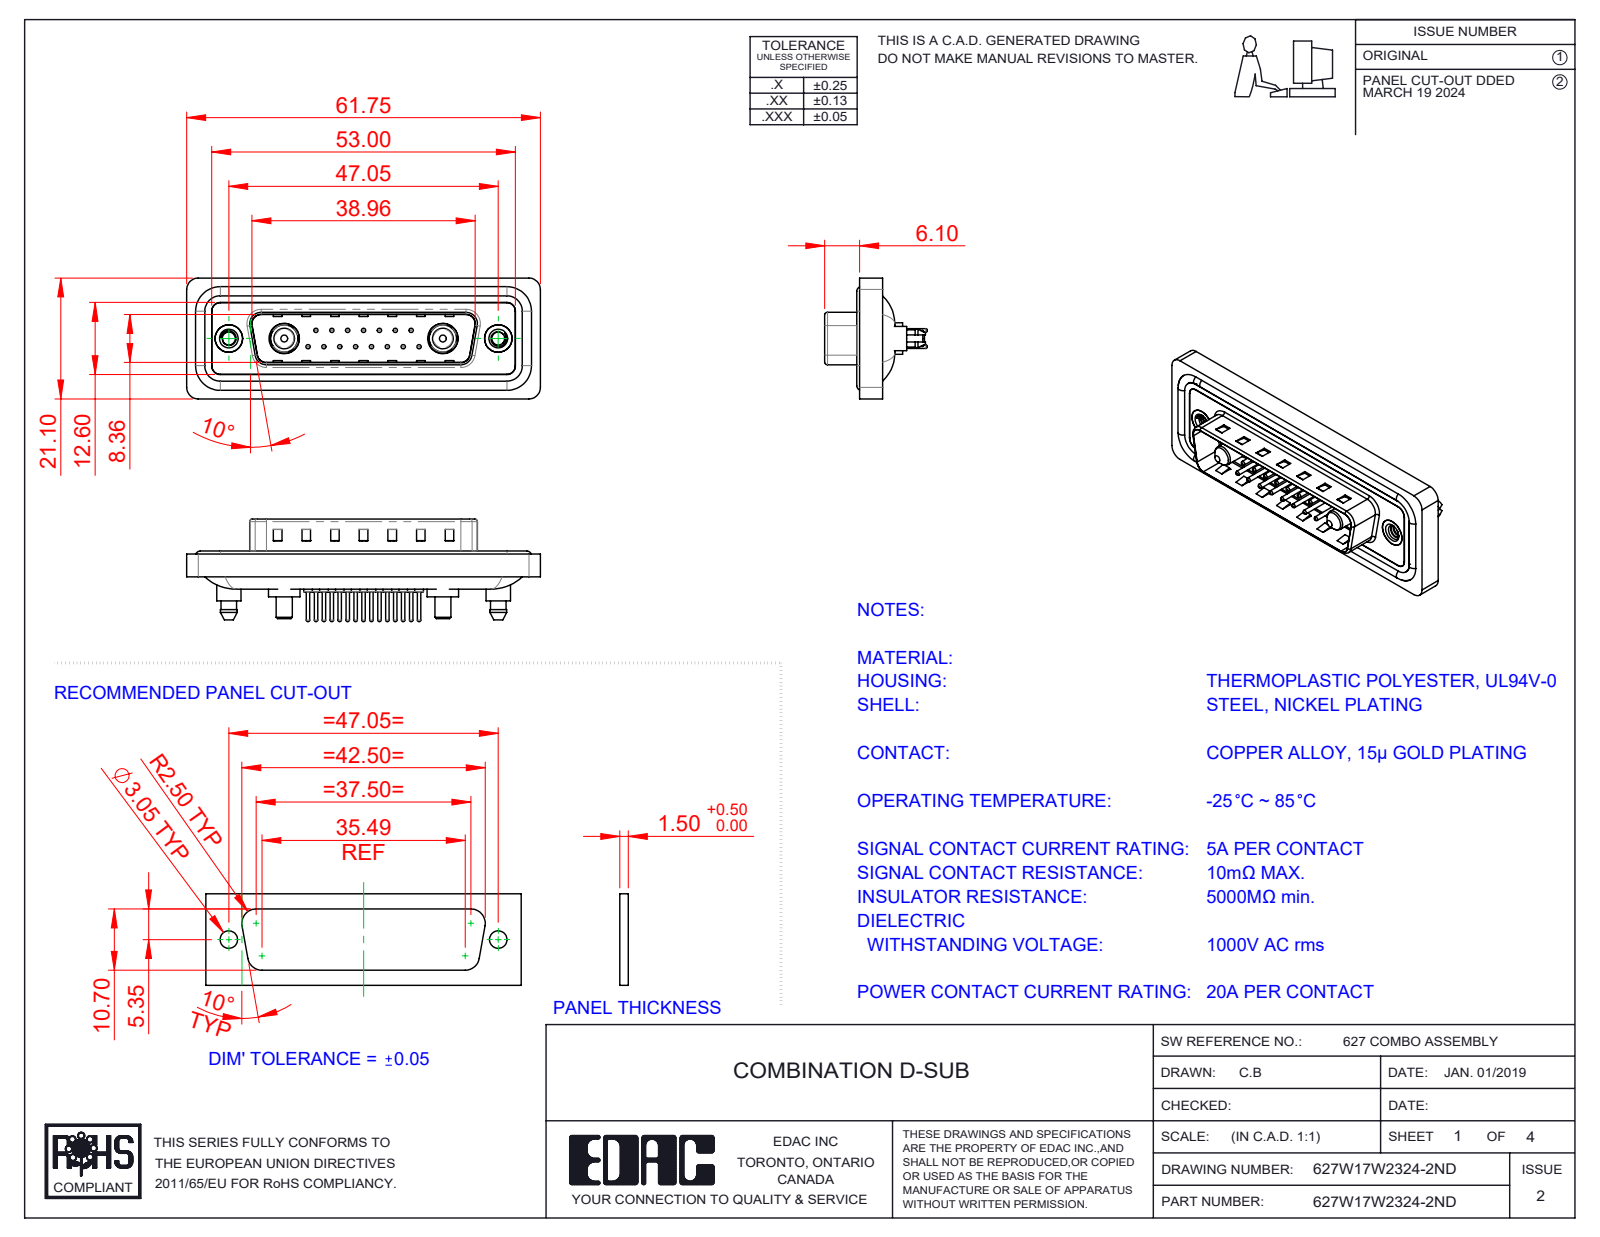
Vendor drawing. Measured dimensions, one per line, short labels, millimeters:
name: 627Combo Threaded Boardlock_D; 627Combo Shell Rear_25 Contacts; 627Combo Contact Row 1_24; Power Pin_20A S (+6 more)
written by: SolidWorks 2023 (CONFIG_CONTROL_DESIGN)
unit: mm
bodies: 26 solids, 1174 faces (350 planar, 476 cylindrical, 348 other)
size: 61.75 × 21.1 × 17.9
volume: 7 401 mm³; area: 12 250 mm²
holes: 15× ⌀0.75, 15× ⌀1.6, 15× ⌀2, 2× ⌀2.26, 2× ⌀4, 2× ⌀4.8, 2× ⌀4.85, 2× ⌀5, 2× ⌀5.3
bosses: 15× ⌀1.5, 15× ⌀0.6, 4× ⌀1.6, 2× ⌀5.5, 2× ⌀5.4, 2× ⌀5.2, 2× ⌀4.9, 2× ⌀4.75
rounds: 24× R1.5, 18× R2, 10× R1.6, 8× R0.5, 4× R0.25, 4× R0.6, 4× R0.65, 4× R0.9
face distances: 0.4, 1.5, 1.1, 1.6, 0.5, 3.1, 2.9, 0.82, 9.58, 4.1
hole spacings: 3.16, 2.77, 5.54, 8.31, 5.04, 7.49, 11.08, 5.03
